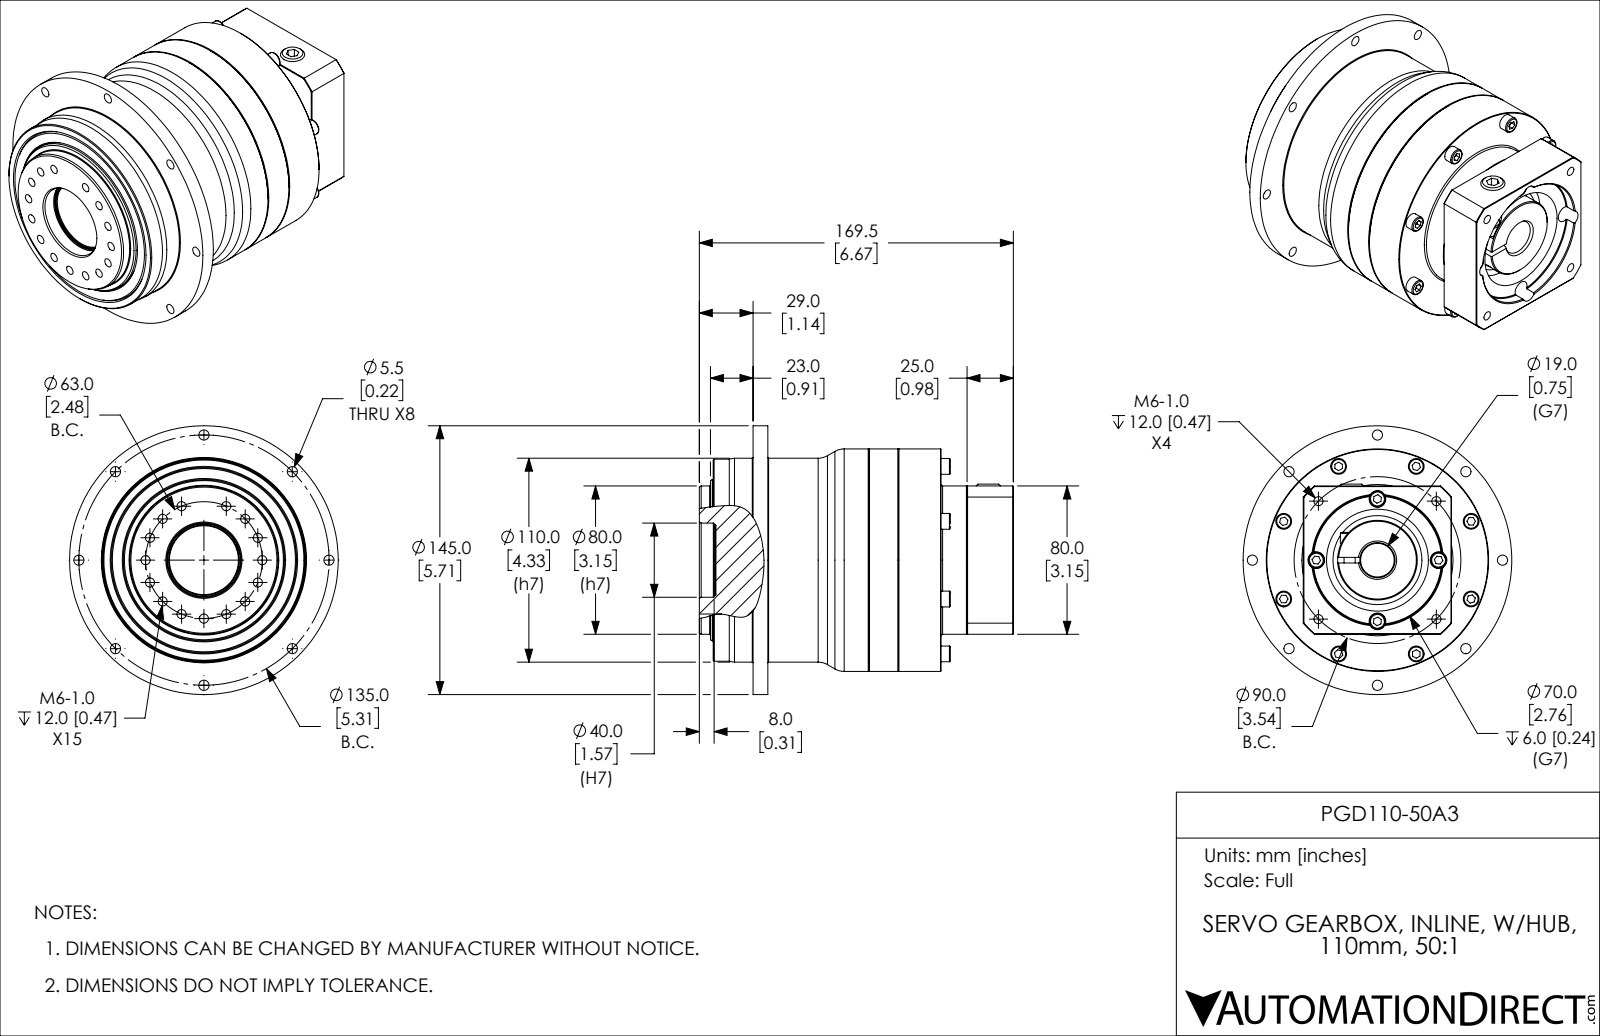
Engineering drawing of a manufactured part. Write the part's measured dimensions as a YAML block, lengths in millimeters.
part_name: "PGD110-50A3"
step_written_by: "SolidWorks 2021 (CONFIG_CONTROL_DESIGN)"
units: millimeters
bodies: {solids: 1, faces: 485, planar: 152, cylindrical: 153, other: 180}
overall_size: [169.5, 145, 145]
volume: 1526000
surface_area: 116800
round_holes:
  - {diameter: 4.9, count: 13}
  - {diameter: 5.5, count: 12}
  - {diameter: 4.9, count: 7}
  - {diameter: 9, count: 4}
  - {diameter: 6.5, count: 1}
  - {diameter: 10.5, count: 1}
  - {diameter: 19, count: 1}
  - {diameter: 38, count: 1}
  - {diameter: 40, count: 1}
  - {diameter: 48, count: 1}
  - {diameter: 55, count: 1}
  - {diameter: 70, count: 1}
round_bosses_or_shafts:
  - {diameter: 8.5, count: 12}
  - {diameter: 5, count: 4}
  - {diameter: 145, count: 1}
  - {diameter: 120, count: 1}
  - {diameter: 110, count: 1}
  - {diameter: 109, count: 1}
  - {diameter: 87, count: 1}
  - {diameter: 80, count: 1}
partial_cylinders:
  - {radius: 5.5, count: 1}
  - {radius: 52.5, count: 1}
face_to_face_distances: [8, 93.5, 101.5, 29, 130.5, 37, 80, 7.5, 123, 29.5]
hole_center_spacings: [40.3, 62.6, 74.5, 84.7, 97.4, 12.3, 52.4, 44.6]
